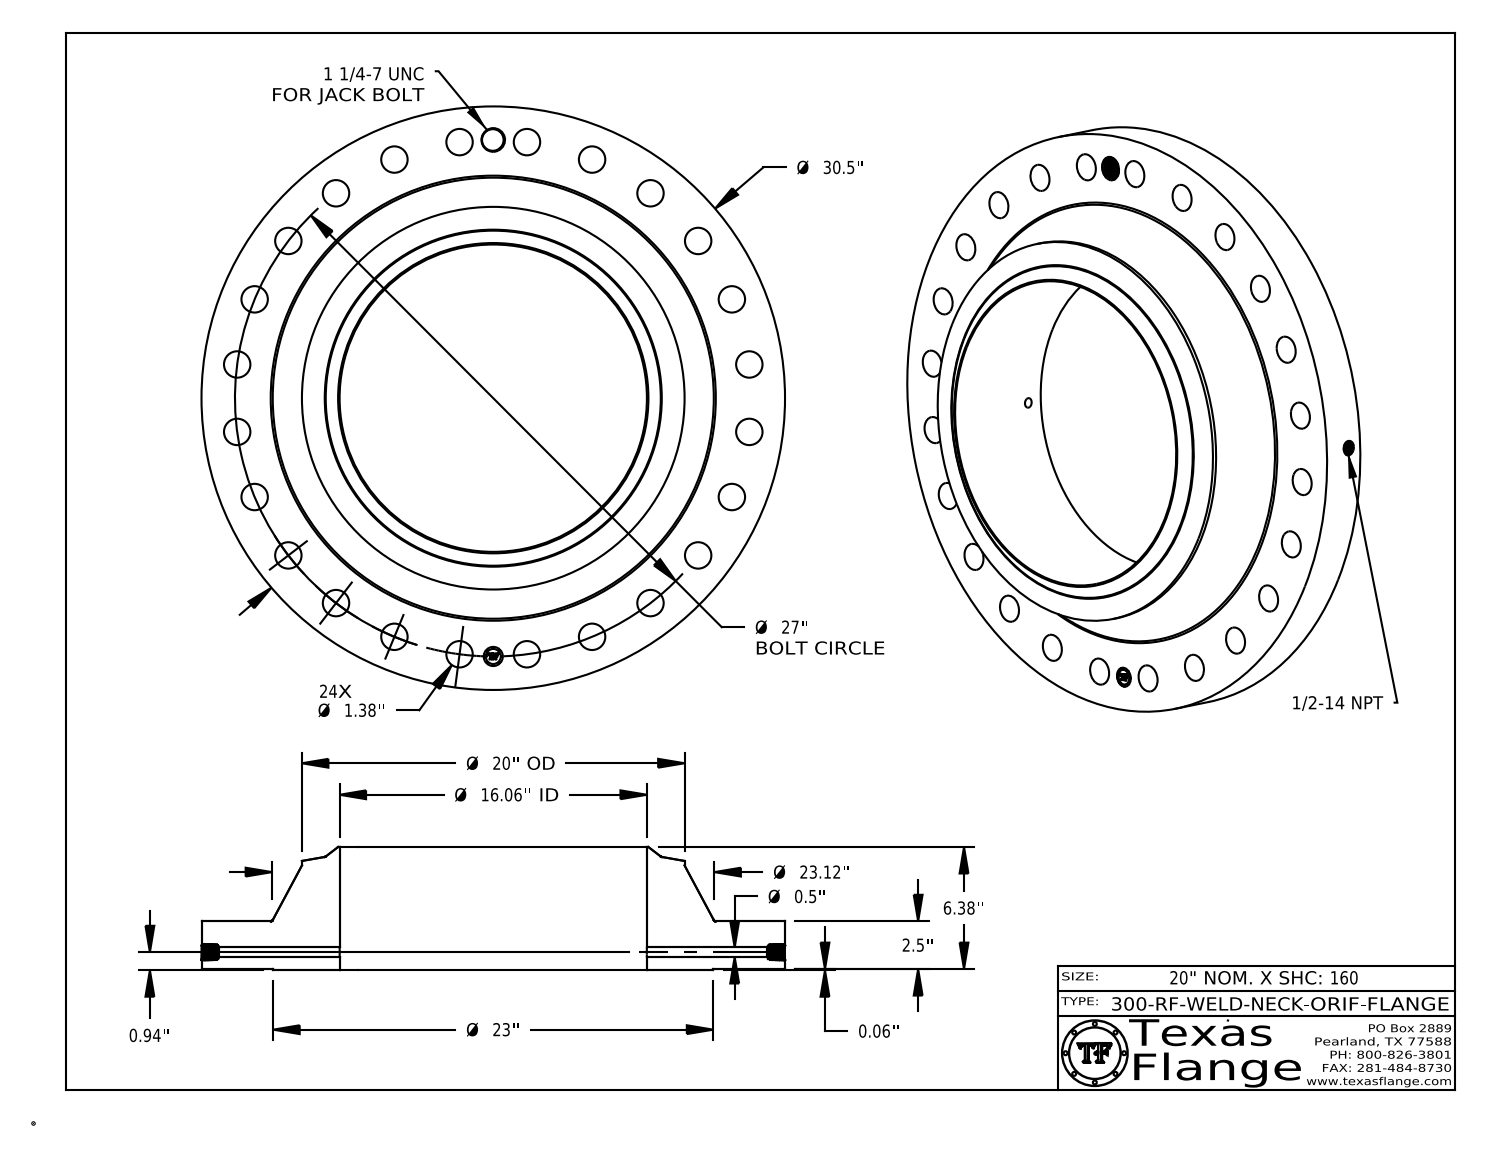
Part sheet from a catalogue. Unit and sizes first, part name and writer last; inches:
Units: inches
Overall size (bounding box): 30.5 × 30.5 × 6.44
Round holes (diameter × count): ⌀1.38 ×24, ⌀0.5 ×1, ⌀0.672 ×1, ⌀1 ×1, ⌀1.109 ×1, ⌀16.062 ×1
Round bosses / shafts (diameter × count): ⌀0.061 ×8, ⌀30.5 ×1, ⌀23 ×1, ⌀20 ×1, ⌀0.788 ×1
Main face-to-face distances: 2.5, 0.06, 2.56, 6.44, 6.38, 3.88, 2.545, 2.485, 0.015, 3.895
Hole centre spacings: 13.5, 23.383, 24.945, 21.42, 3.524, 6.988, 19.092, 26.08
Volume: 1 766 in³ · Surface area: 1 993 in²
Bodies: 1 solid, 822 faces (369 planar, 131 cylindrical, 322 other)
Part name (STEP PRODUCT): 300-RF-WELD-NECK
STEP written by: CATIA V5 STEP AP214 (AUTOMOTIVE_DESIGN)
